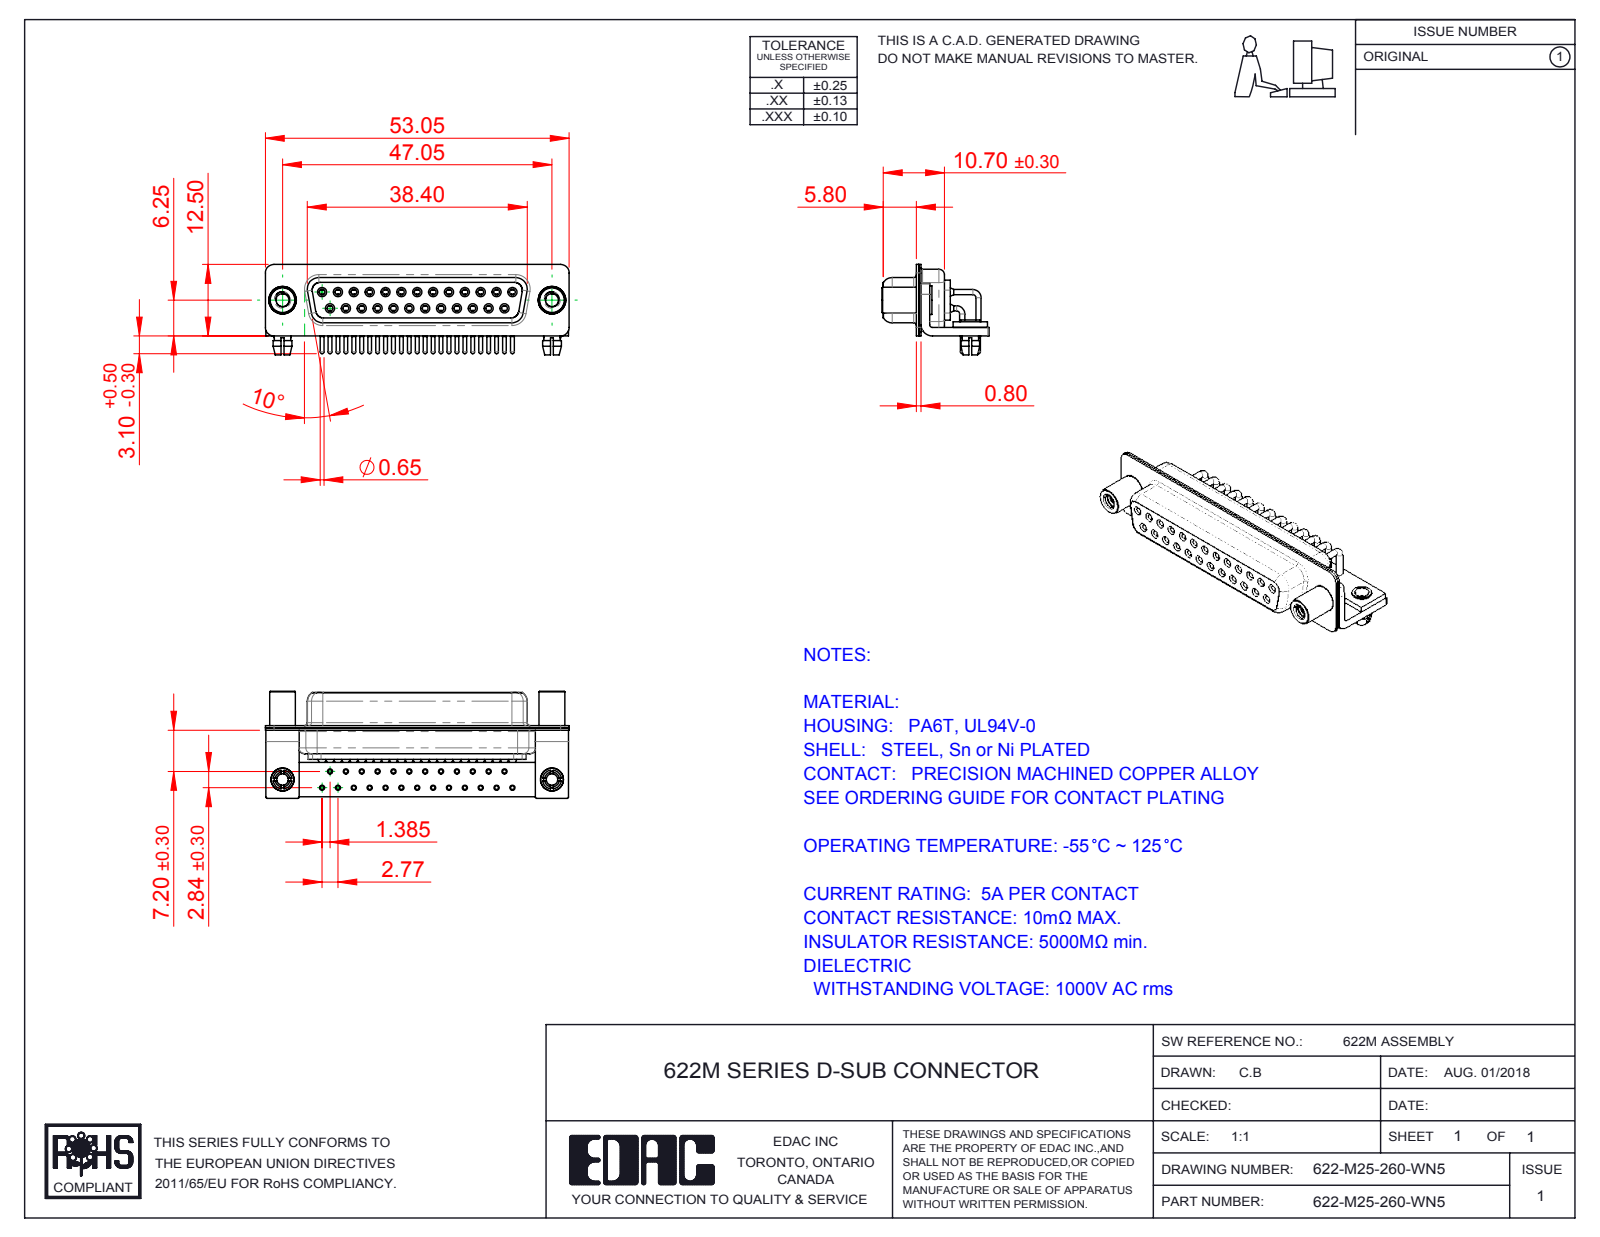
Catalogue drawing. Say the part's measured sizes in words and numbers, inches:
The part is named "622M Stabilizer Bracket; 622M Contact Row 2; 622M Contact Row 1; 622M Shell Rear_25 Contacts (+6 more)". Its 3-D file was written by "SolidWorks 2016 (CONFIG_CONTROL_DESIGN)". It is 35 solids with 1846 faces: 518 planar, 858 cylindrical and 470 other. Overall it measures 2.089 by 0.736 by 0.622 inches. Its volume is 0.277 cubic inches and its surface area 17.61 square inches. Round holes: 27 of diameter 0.079, 25 of diameter 0.035, 25 of diameter 0.039, 25 of diameter 0.043, 25 of diameter 0.067, 25 of diameter 0.071, 2 of diameter 0.089, 2 of diameter 0.098, 2 of diameter 0.126, 2 of diameter 0.157, 2 of diameter 0.189. Round bosses or shafts: 27 of diameter 0.035, 25 of diameter 0.063, 25 of diameter 0.059, 25 of diameter 0.026, 2 of diameter 0.197, 2 of diameter 0.193, 2 of diameter 0.177, 2 of diameter 0.157. Partial cylindrical surfaces (rounded edges, fillets, slot ends): 16 of radius 0.01, 16 of radius 0.059, 13 of radius 0.079, 8 of radius 0.053, 8 of radius 0.063, 5 of radius 0.02, 4 of radius 0.024, 4 of radius 0.026. The main face-to-face distances are 0.016, 0.091, 0.075, 0.057, 0.352, 0.033, 0.031, 0.244, 0.368, 0.039. The hole center spacings are 0.124, 0.109, 0.218, 0.327, 0.436, 0.545, 0.654, 0.198.
